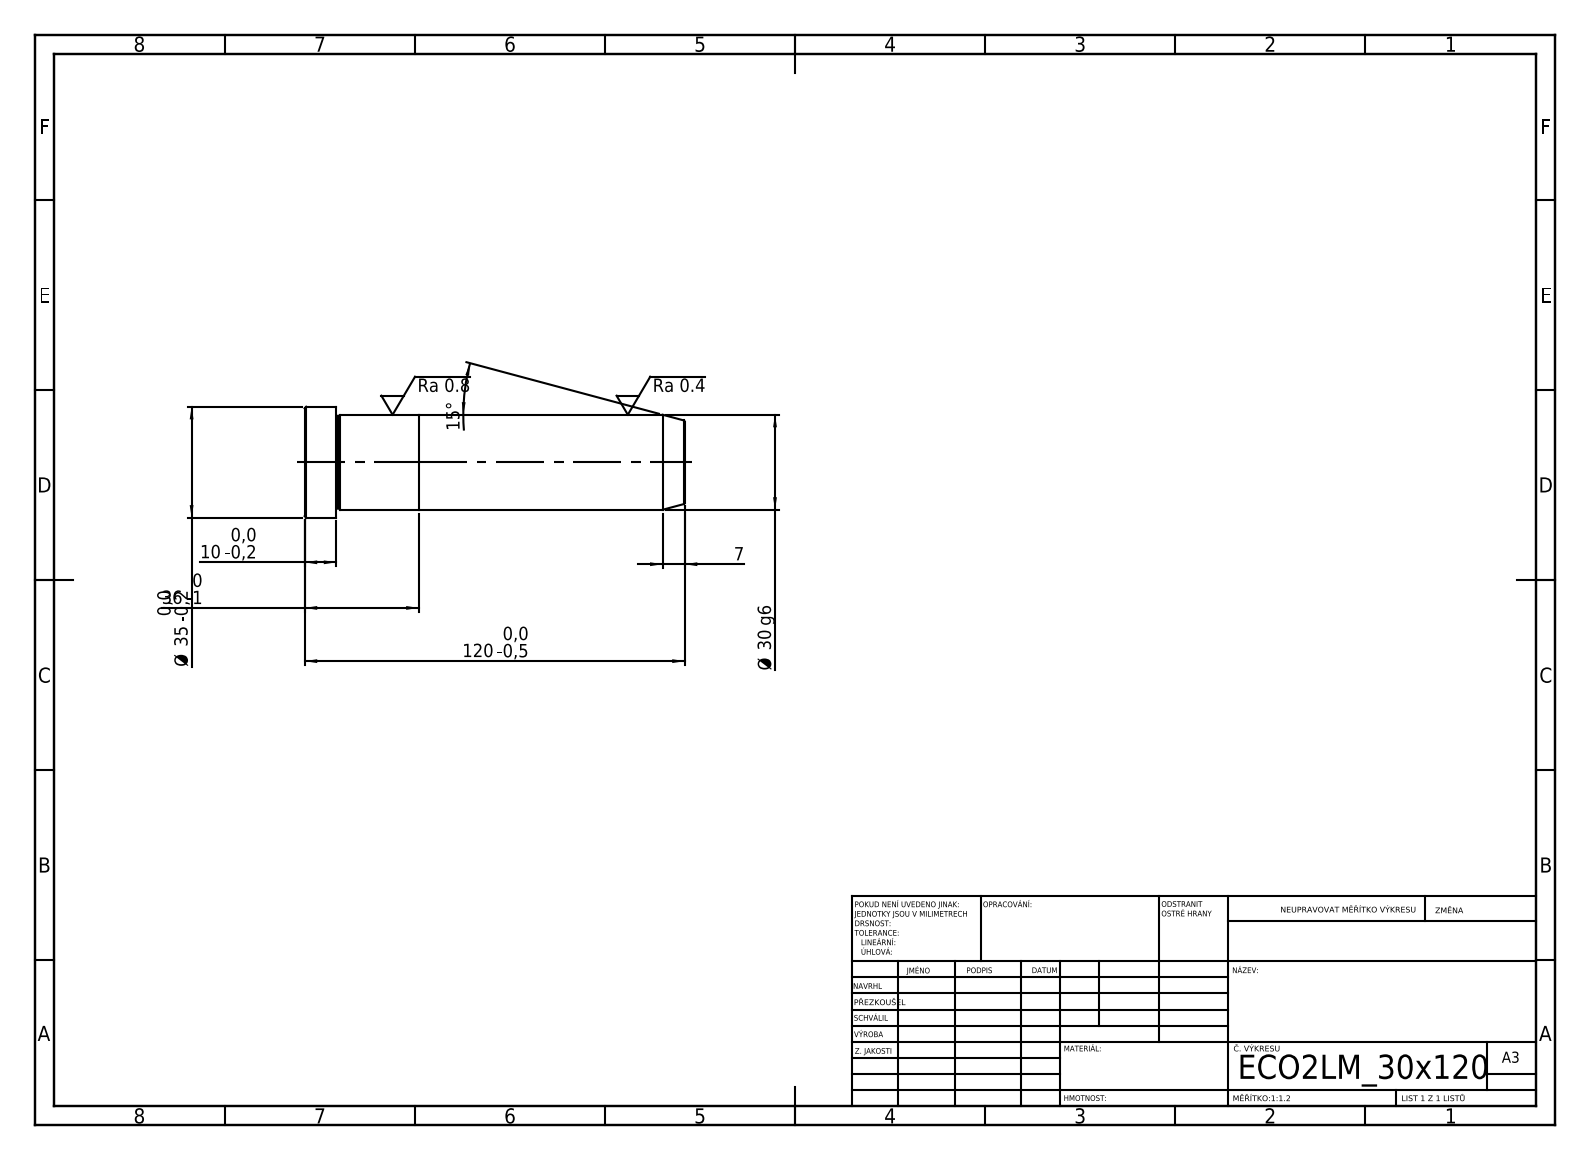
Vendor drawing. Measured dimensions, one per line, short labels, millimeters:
written by: SolidWorks 2019 (CONFIG_CONTROL_DESIGN)
unit: mm
bodies: 2 solids, 21 faces (5 planar, 6 cylindrical, 10 other)
size: 120 × 35 × 35
volume: 86 730 mm³; area: 14 628 mm²
bosses: 1× ⌀35, 1× ⌀30
face distances: 36, 84, 120, 110, 26, 10
